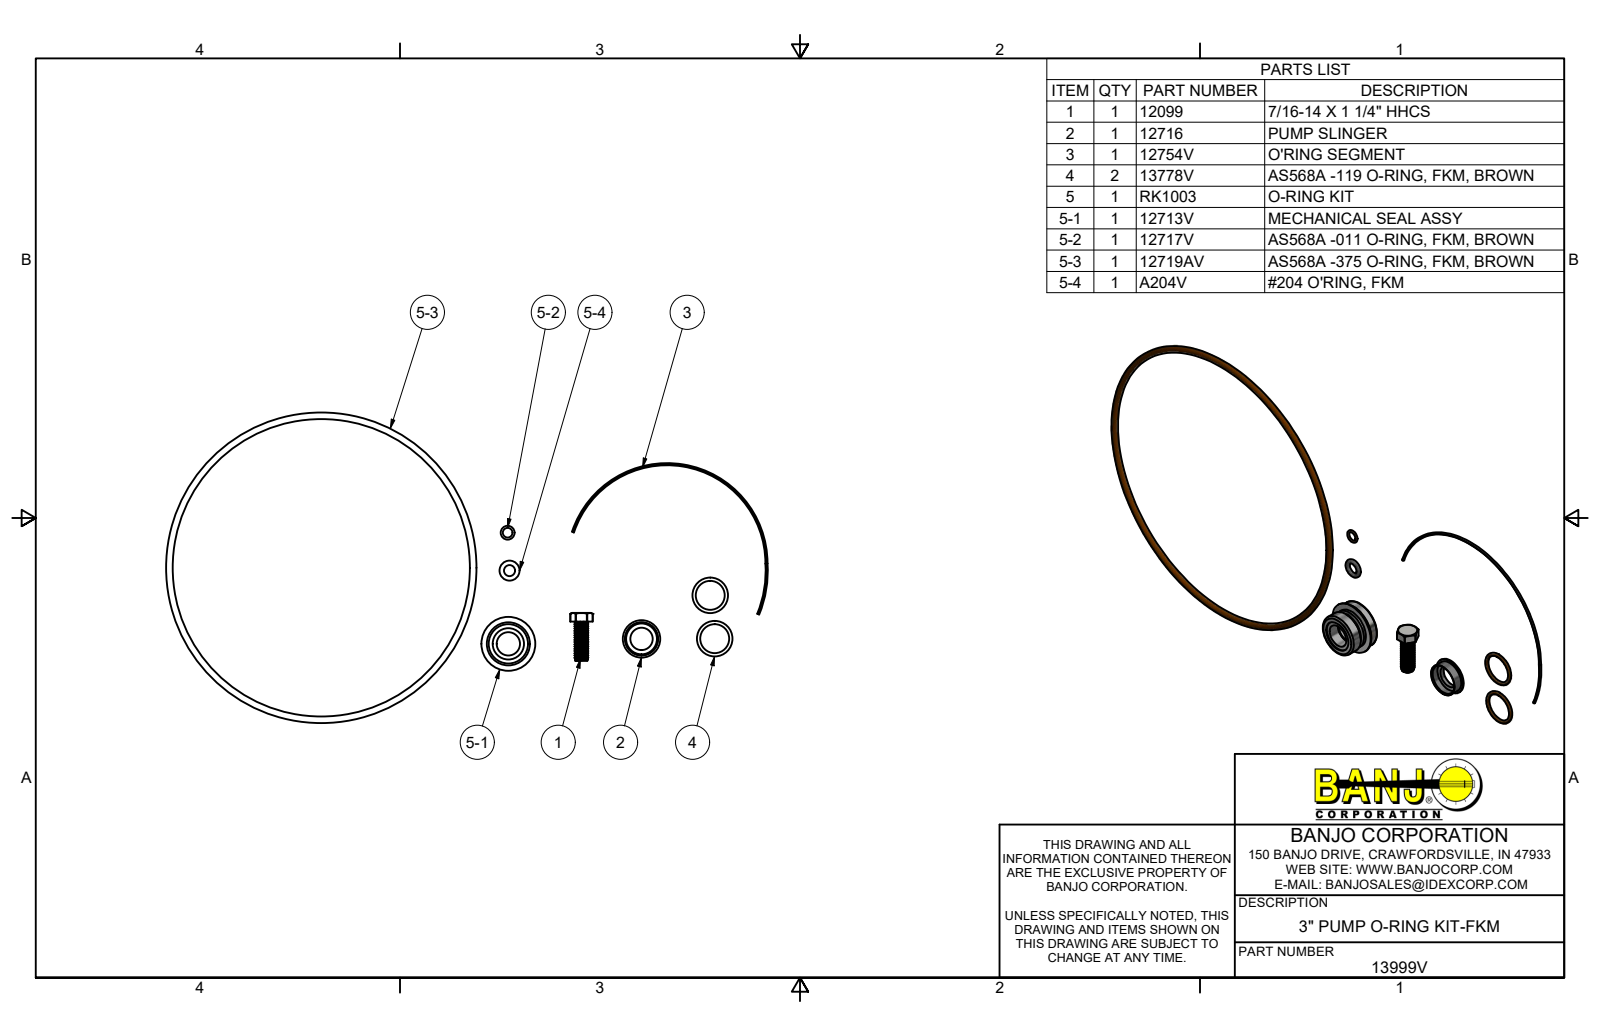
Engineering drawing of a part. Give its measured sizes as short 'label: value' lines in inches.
name: 13999V; 12099; 12716; 12754V (+7 more)
written by: Autodesk Inventor 2019 (AUTOMOTIVE_DESIGN)
unit: in
bodies: 10 solids, 140 faces (26 planar, 59 cylindrical, 55 other)
size: 19.177 × 9.895 × 1.155
volume: 2.689 in³; area: 45.76 in²
holes: 1× ⌀0.719, 1× ⌀0.75, 1× ⌀0.813, 1× ⌀0.875, 1× ⌀0.98, 1× ⌀1
bosses: 17× ⌀0.379, 1× ⌀1.72, 1× ⌀1.575, 1× ⌀1.375, 1× ⌀1.313, 1× ⌀1.305, 1× ⌀1.19, 1× ⌀1.125
rounds: 1× R0.19, 1× R0.356
face distances: 0.38, 0.031, 0.615, 0.235, 0.375, 1.021, 0.641, 0.406, 0.261, 0.119
hole spacings: 4.249
